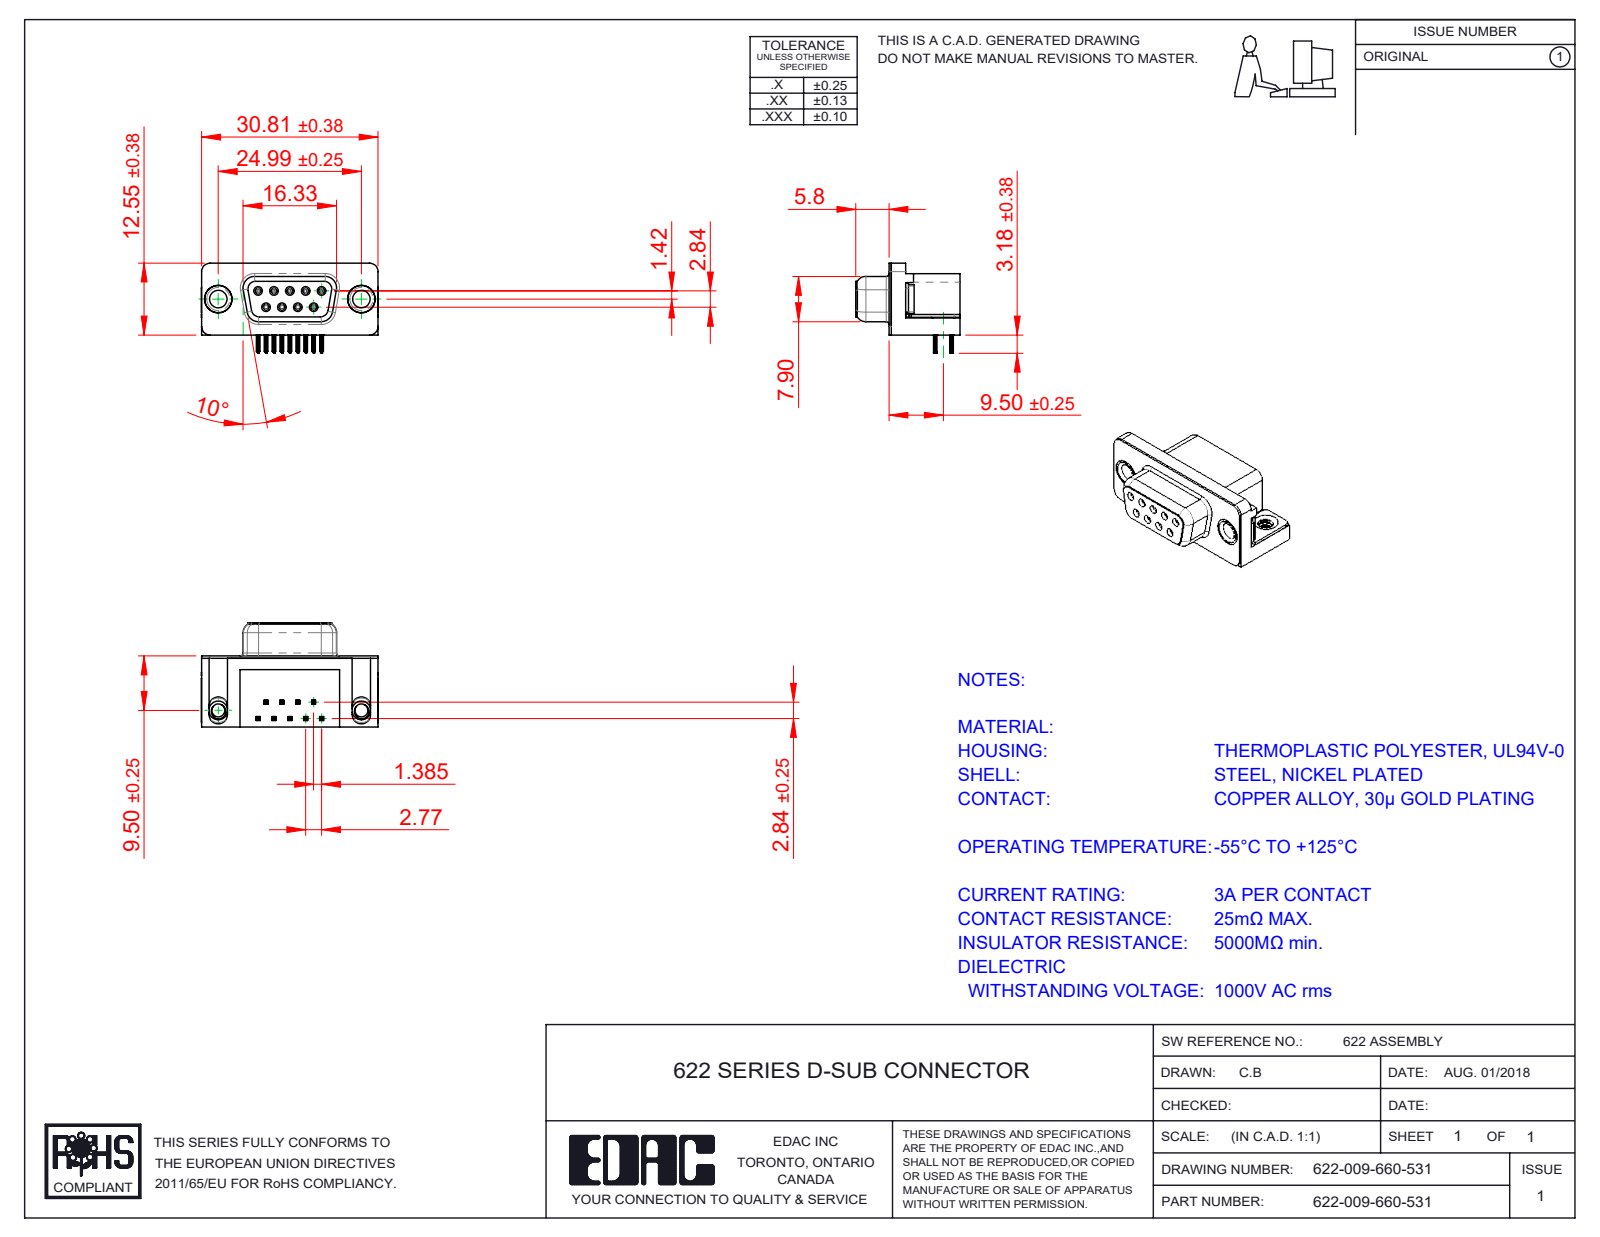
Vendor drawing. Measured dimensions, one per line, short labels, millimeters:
name: 622 Contact Top; 622 Shell_9 Socket; 622 Thru Hole Rivet; 622 Socket Bottom (+3 more)
written by: SolidWorks 2016 (CONFIG_CONTROL_DESIGN)
unit: mm
bodies: 15 solids, 1572 faces (716 planar, 406 cylindrical, 450 other)
size: 30.89 × 18.2 × 16.25
volume: 3 713 mm³; area: 5 056 mm²
holes: 9× ⌀0.8, 9× ⌀0.9, 2× ⌀3.05, 2× ⌀4, 2× ⌀4.8, 2× ⌀5
bosses: 9× ⌀1.2, 2× ⌀4.9, 2× ⌀4.75, 2× ⌀3.85
rounds: 72× R0.1, 36× R0.15, 18× R0.35, 18× R1, 10× R0.5, 9× R0.34, 8× R0.25, 8× R1.35
face distances: 0.4, 12, 12.4, 0.35, 2.9, 2.5, 6.2, 10.34, 0.5, 9.5
hole spacings: 3.16, 2.77, 5.54, 5.03, 5.04, 8.31, 7.48, 7.49
